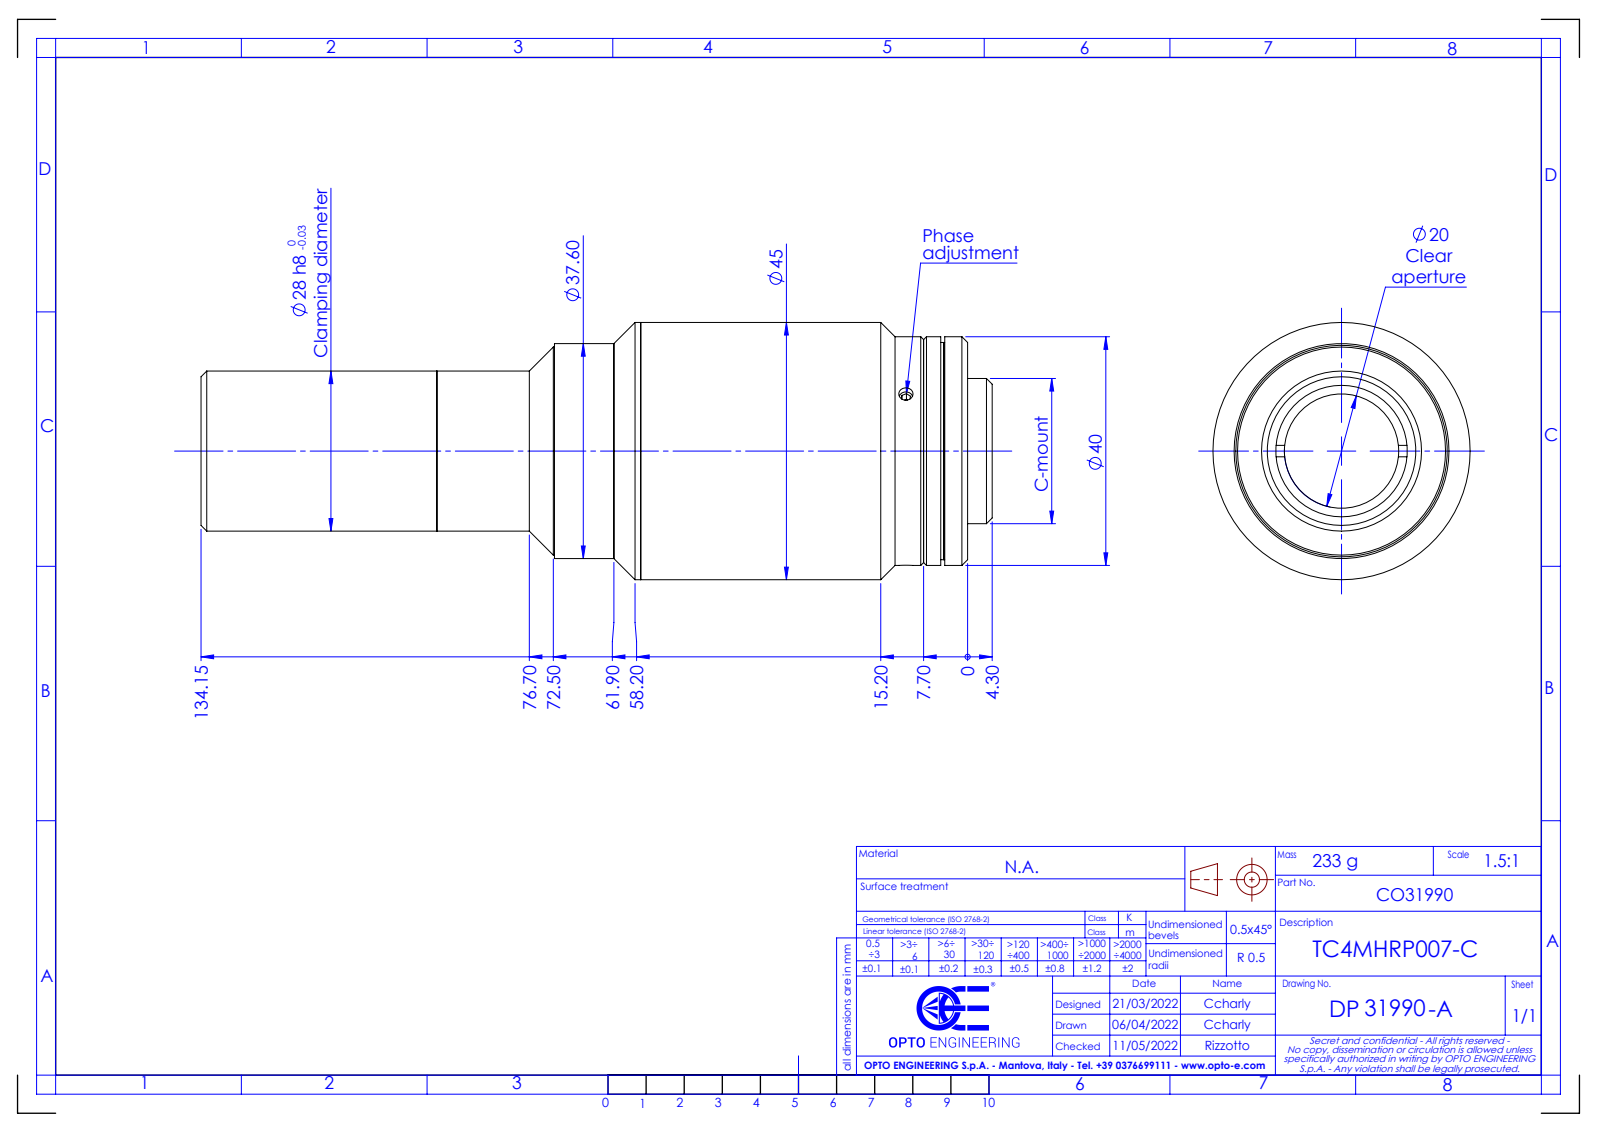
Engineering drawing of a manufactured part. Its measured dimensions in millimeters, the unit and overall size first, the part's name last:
Units: millimetres
Overall size (bounding box): 138.45 × 45 × 45
Round holes (diameter × count): ⌀2.5 ×3, ⌀20 ×1, ⌀22.5 ×1, ⌀23 ×1
Round bosses / shafts (diameter × count): ⌀45 ×1, ⌀40 ×1, ⌀37.6 ×1, ⌀36.4 ×1, ⌀28 ×1, ⌀25.4 ×1
Main face-to-face distances: 0.7, 4.7, 4, 3, 3.7, 7.7, 85.17, 88.17, 88.87, 92.87
Bodies: 0 solids, 83 faces (31 planar, 32 cylindrical, 20 other)
Part name (STEP PRODUCT): DP31990-A_TC4MHRP007-C
STEP written by: SolidWorks 2021 (CONFIG_CONTROL_DESIGN)
